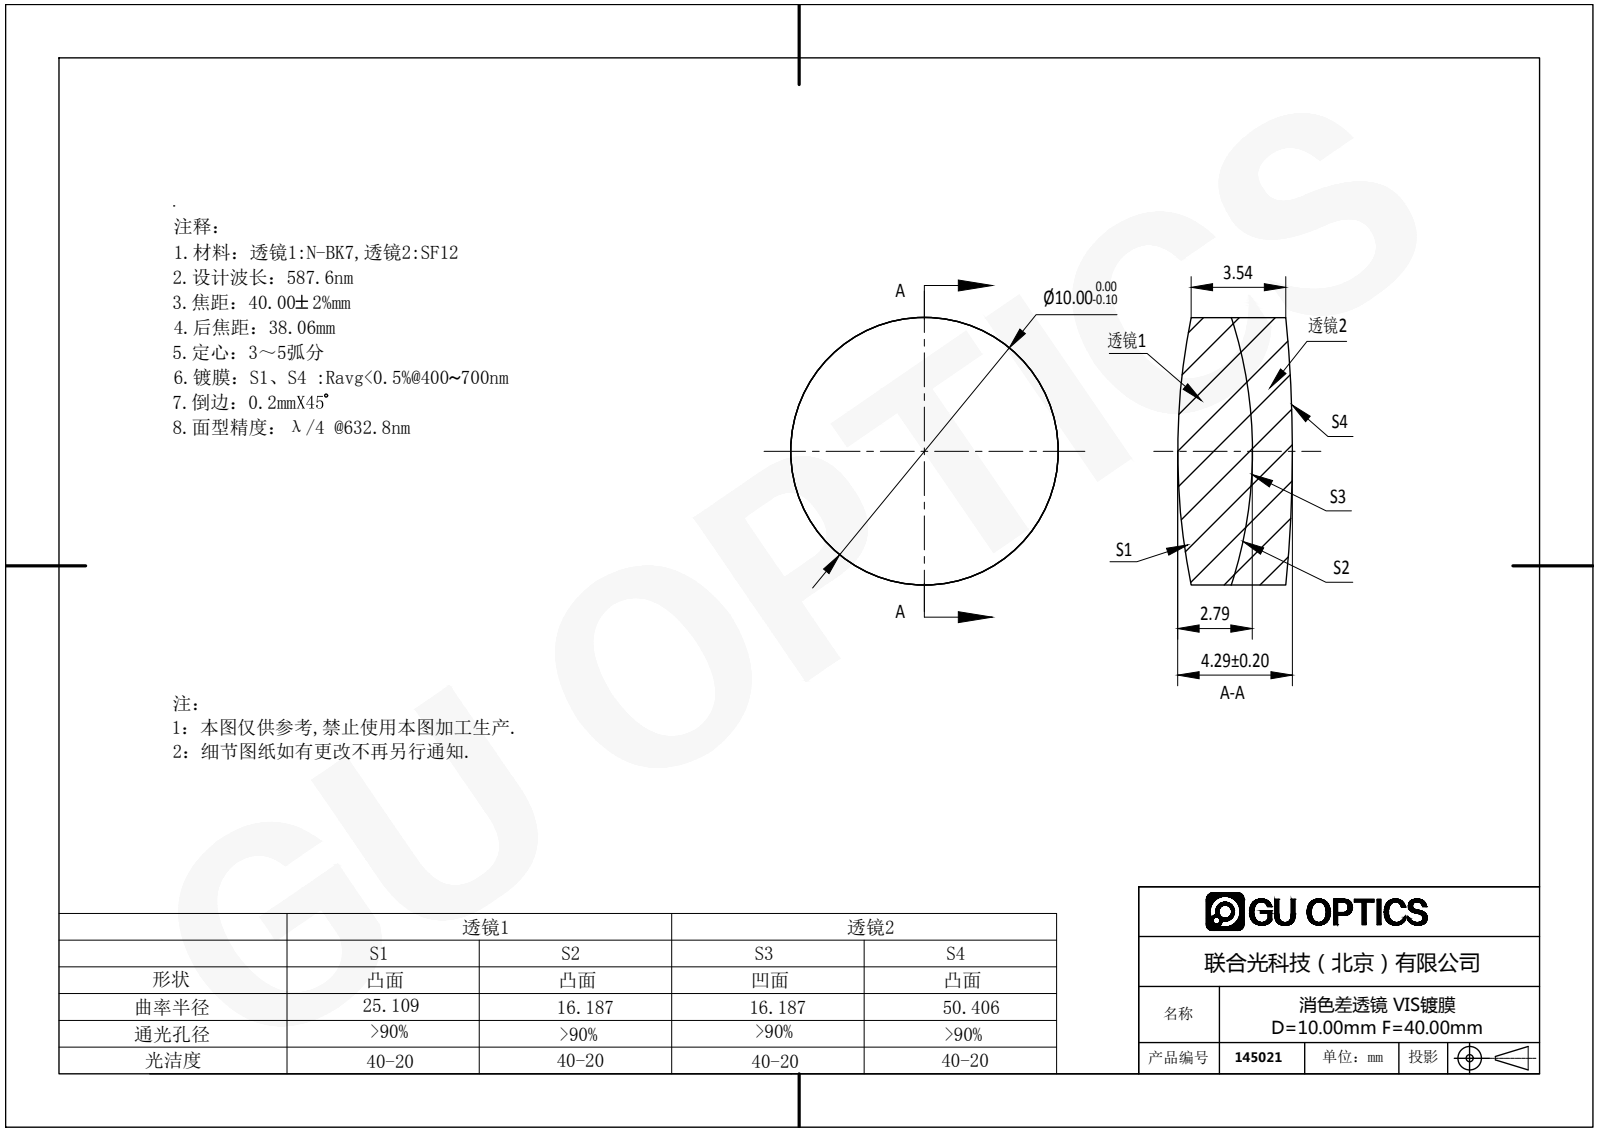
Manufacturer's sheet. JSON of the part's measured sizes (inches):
{"part_name": "145021", "step_written_by": "SolidWorks 2016 (AUTOMOTIVE_DESIGN)", "units": "inches", "bodies": {"solids": 2, "faces": 12, "planar": 0, "cylindrical": 4, "other": 8}, "overall_size": [0.394, 0.394, 0.169], "volume_in3": 0.019, "surface_area_in2": 0.667, "round_bosses_or_shafts": [[0.394, 1]]}
